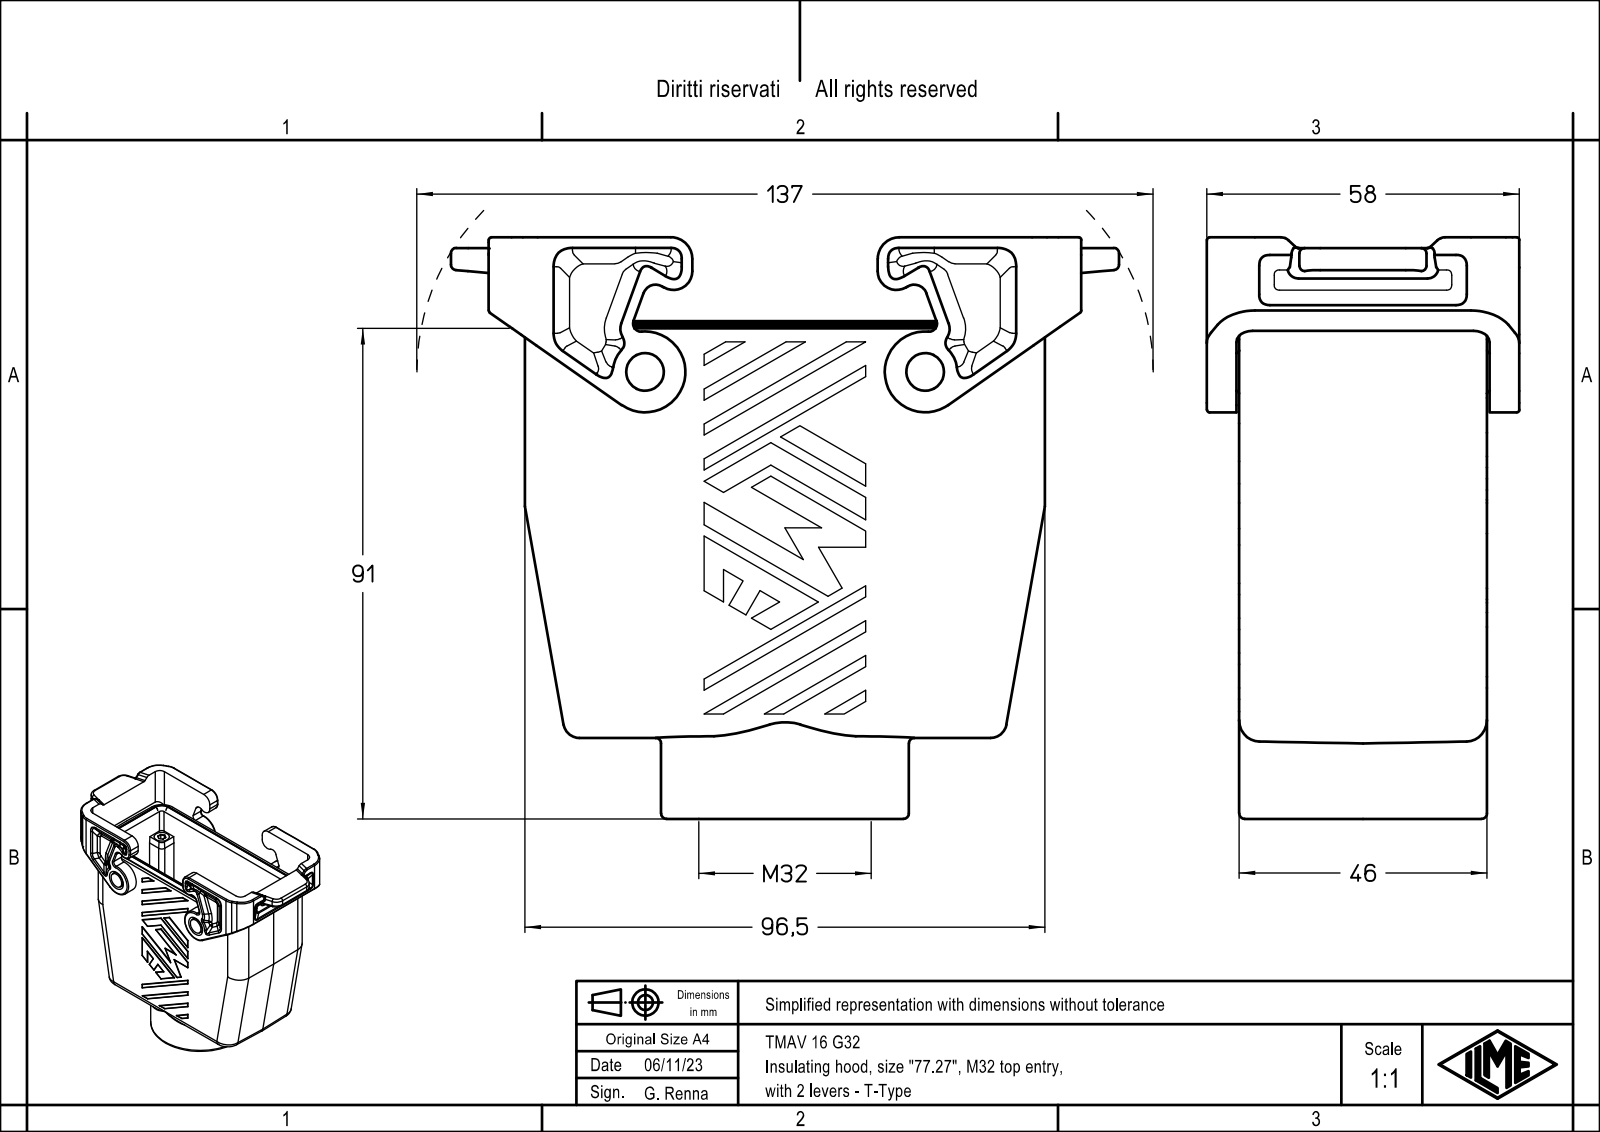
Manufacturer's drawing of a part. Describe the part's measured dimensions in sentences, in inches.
The part is named "TMAV_16_G32". Its 3-D file was written by "Creo Elements/Direct Modeling 18.0B 02-Dec-2011 (C) Parametric Technology GmbH (AUTOMOTIVE_DESIGN)". It is 1 solid with 723 faces: 485 planar, 210 cylindrical and 28 other. Overall it measures 4.827 by 4.248 by 2.283 inches. Its volume is 9.7 cubic inches and its surface area 102 square inches. Round holes: 4 of diameter 0.202, 4 of diameter 0.256, 2 of diameter 0.236, 2 of diameter 0.394, 1 of diameter 1.102, 1 of diameter 1.26. Round bosses or shafts: 2 of diameter 0.276, 1 of diameter 1.811. Partial cylindrical surfaces (rounded edges, fillets, slot ends): 10 of radius 0.118, 10 of radius 0.276, 8 of radius 0.039, 8 of radius 0.059, 8 of radius 0.071, 4 of radius 0.079, 2 of radius 0.04, 2 of radius 0.094. The main face-to-face distances are 1.811, 0.02, 1.831, 0.039, 1.791, 0.098, 0.217, 0.236, 0.256, 2.028. The hole center spacings are 1.615, 0.37, 1.063, 2.387, 3.051, 3.231, 2.047, 2.717.
